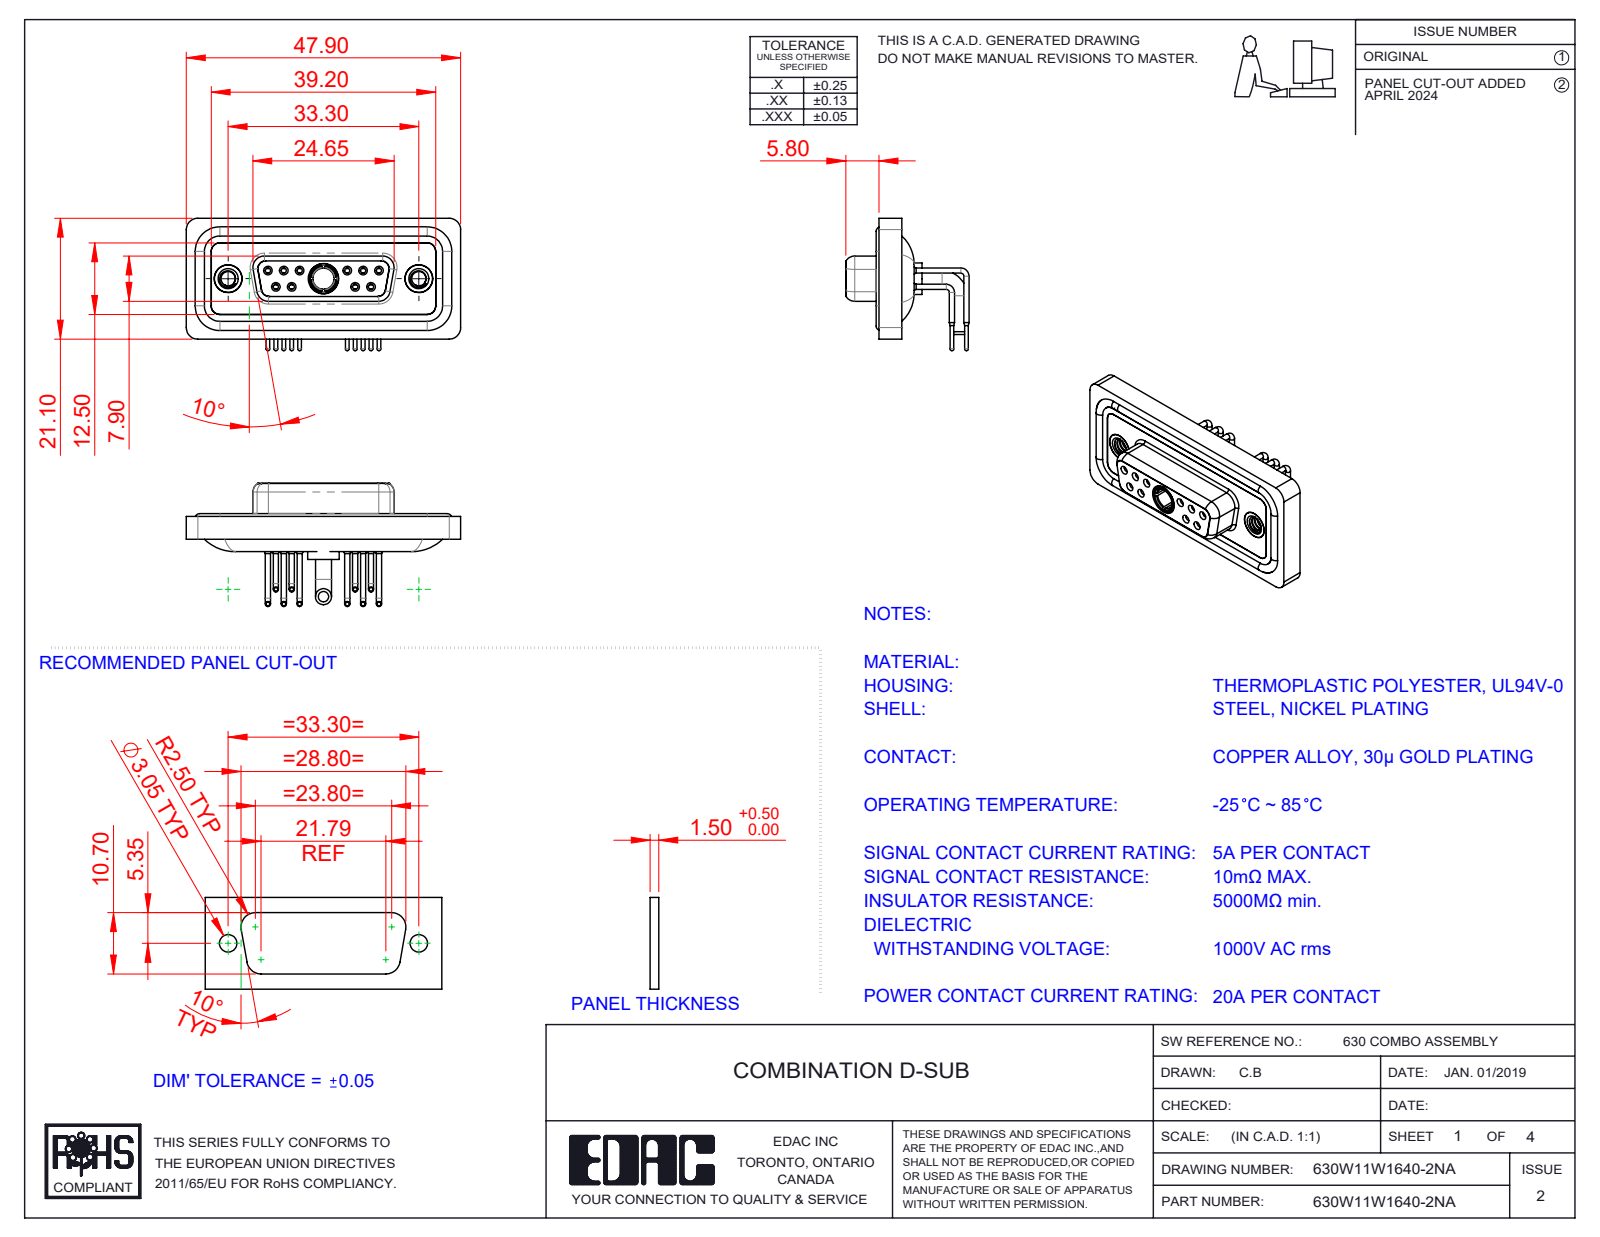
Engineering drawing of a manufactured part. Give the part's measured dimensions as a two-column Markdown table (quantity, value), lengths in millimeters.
| quantity | value |
| --- | --- |
| part name | 630Combo Contact Row 2_50 Contacts; 630Combo Contact Row 1_50 Contacts; Power Socket_20A RA; 630Combo Shell Rear_15 Contacts (+5 more) |
| STEP written by | SolidWorks 2023 (CONFIG_CONTROL_DESIGN) |
| units | millimeters |
| bodies | 19 solids, 988 faces (284 planar, 441 cylindrical, 263 other) |
| overall size | 47.9 × 23.12 × 21.53 |
| volume | 6 210 mm³ |
| surface area | 10 474 mm² |
| round holes (diameter × count) | 0.9 × 10, 1.1 × 10, 1.5 × 10, 2 × 10, 1.7 × 6, 1.6 × 4, 4.85 × 3, 2.5 × 2, 4 × 2, 4.05 × 2, 5 × 2, 3.7 × 1 |
| round bosses / shafts (diameter × count) | 1.6 × 10, 0.9 × 10, 0.65 × 10, 4.95 × 2, 4.8 × 2, 2.8 × 2, 5.5 × 1, 5.2 × 1 |
| partial cylindrical surfaces (radius × count) | 2 × 20, 1.5 × 18, 1.35 × 12, 1.6 × 8, 0.25 × 4, 0.5 × 4, 0.6 × 4, 0.65 × 4 |
| main face-to-face distances | 0.4, 1.8, 1.1, 1.6, 2.5, 2.9, 3.1, 3.7, 4.1, 1.5 |
| hole center spacings | 3.16, 2.77, 13.85, 11.08, 16.62, 5.03, 5.04, 5.54 |
